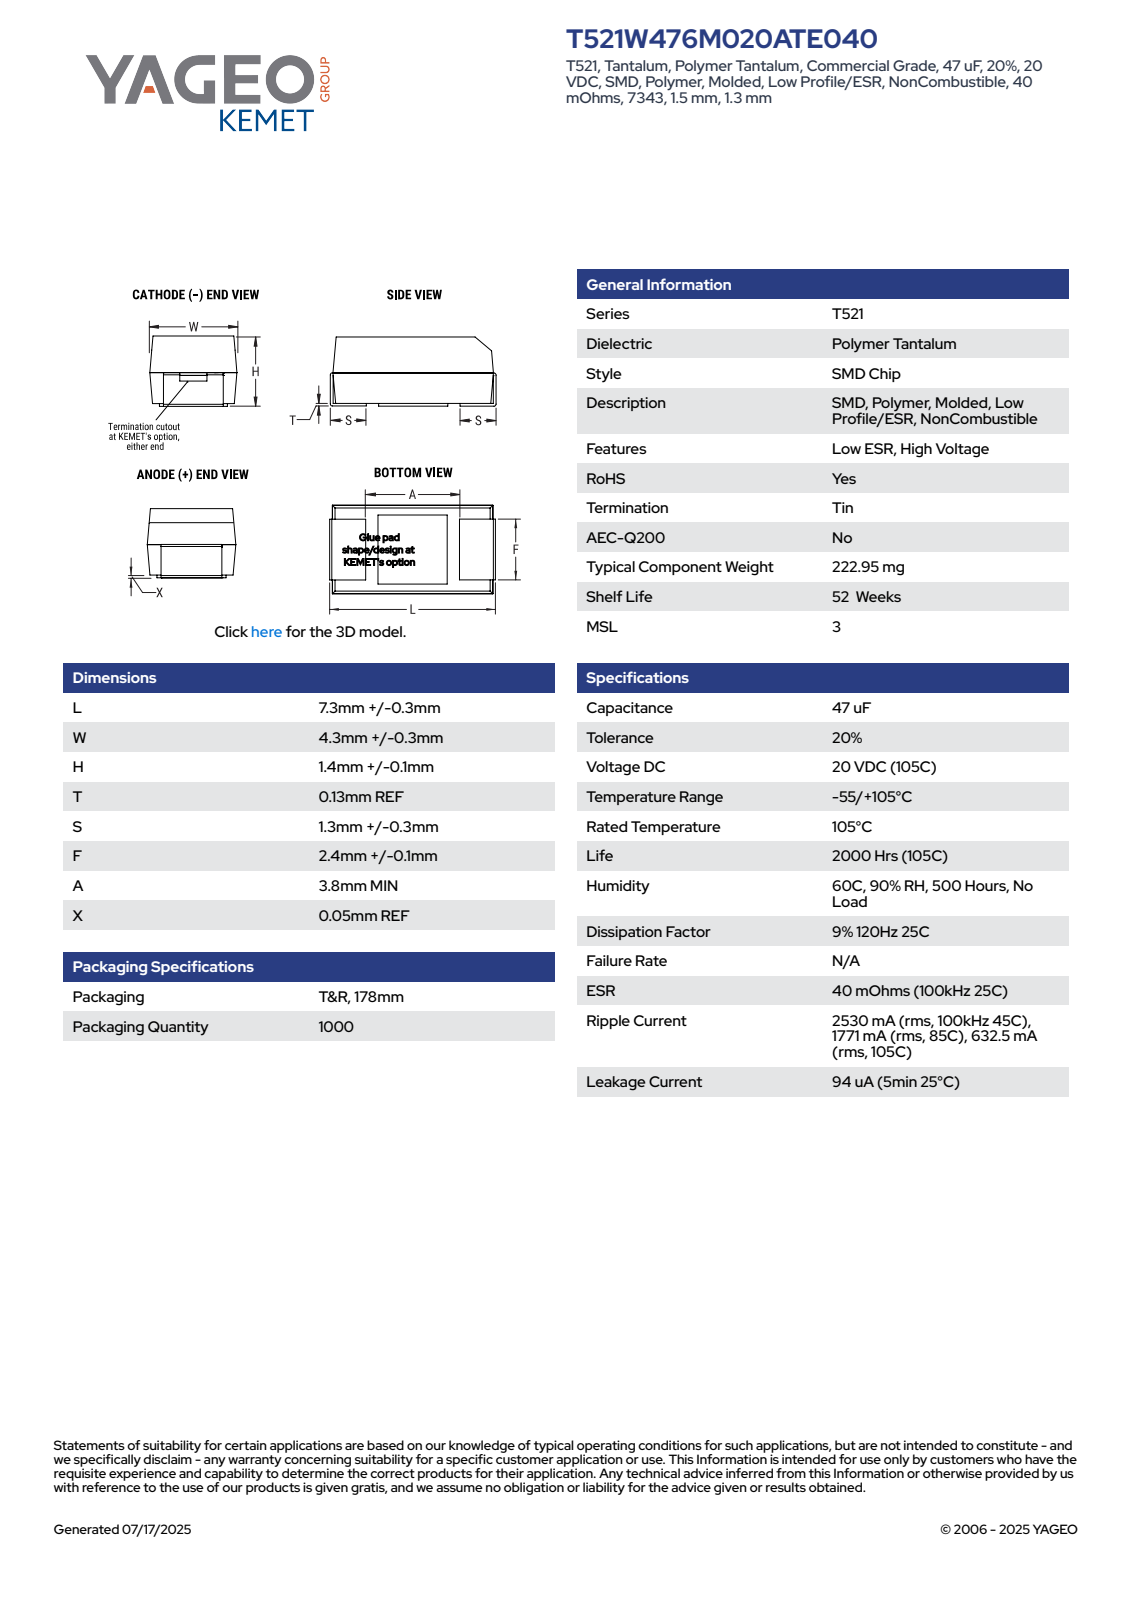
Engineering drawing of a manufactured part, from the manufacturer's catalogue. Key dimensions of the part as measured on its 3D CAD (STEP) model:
Part name (STEP PRODUCT): CTSM_TCM2NBKRPEG_7343_L7.6W4.6H1.5T0.13S1.3F2.5A3.6X0.05
STEP written by: SolidWorks 2014 (AUTOMOTIVE_DESIGN)
Units: millimetres
Bodies: 4 solids, 90 faces (86 planar, 4 cylindrical, 0 other)
Overall size (bounding box): 7.6 × 4.6 × 1.64
Volume: 47 mm³ · Surface area: 104 mm²
Partial cylindrical surfaces — rounded edges, fillets, slot ends (radius × count): R0.1 ×4
Main face-to-face distances: 1.5, 4.34, 1.63, 7.47, 7.6, 7.34, 1.3, 6.3, 1.17, 6.17
